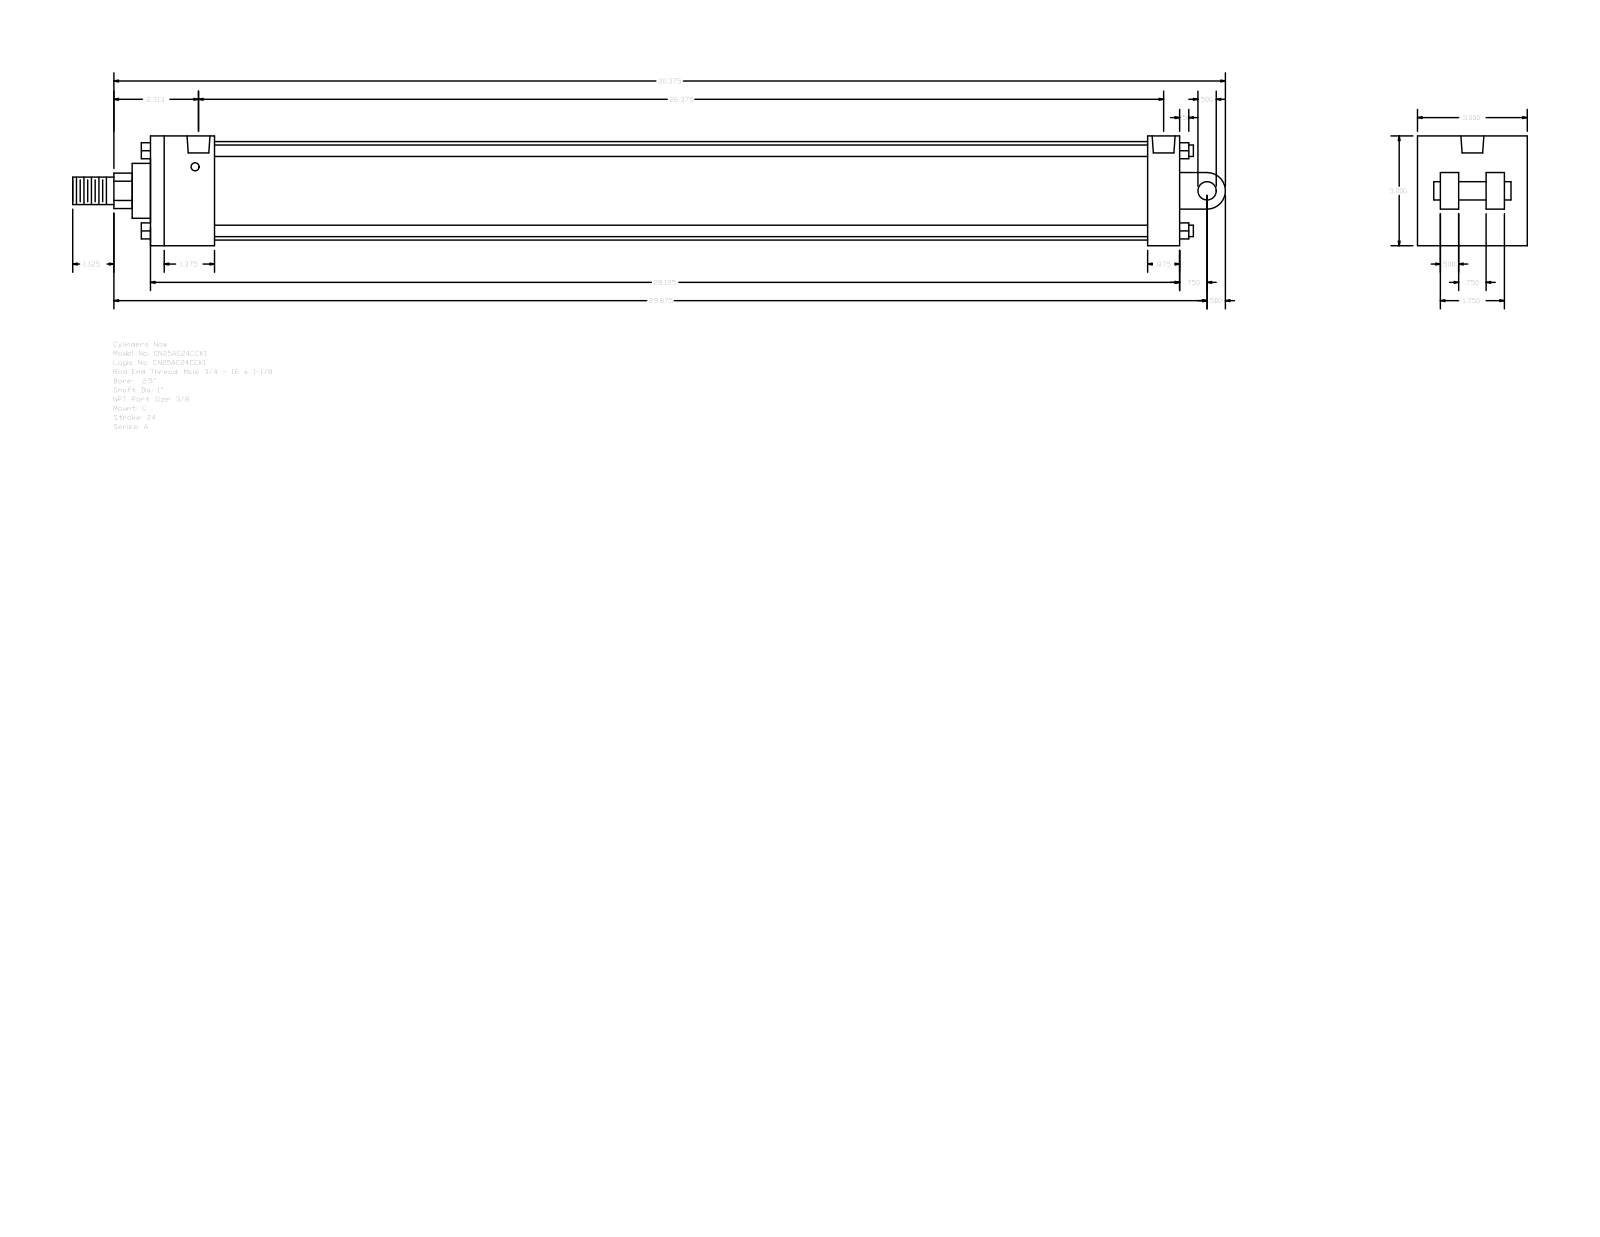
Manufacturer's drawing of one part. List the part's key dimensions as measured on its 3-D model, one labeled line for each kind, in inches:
Part name (STEP PRODUCT): A_C__0250_1
STEP written by: GSSL Pune (CONFIG_CONTROL_DESIGN)
Units: inches
Bodies: 0 solids, 135 faces (102 planar, 33 cylindrical, 0 other)
Overall size (bounding box): 31.5 × 3 × 3
Round holes (diameter × count): ⌀0.219 ×4, ⌀0.627 ×2
Round bosses / shafts (diameter × count): ⌀0.313 ×4, ⌀2.69 ×1, ⌀1.5 ×1, ⌀1 ×1, ⌀0.75 ×1, ⌀0.5 ×1
Partial cylindrical surfaces — rounded edges, fillets, slot ends (radius × count): R0.484 ×1, R0.5 ×1
Main face-to-face distances: 3, 28.125, 0.5, 1.75, 27.25, 25.5, 26.375, 0.875, 0.625, 1
Hole centre spacings: 0.094, 26.469, 26.562, 26.375
